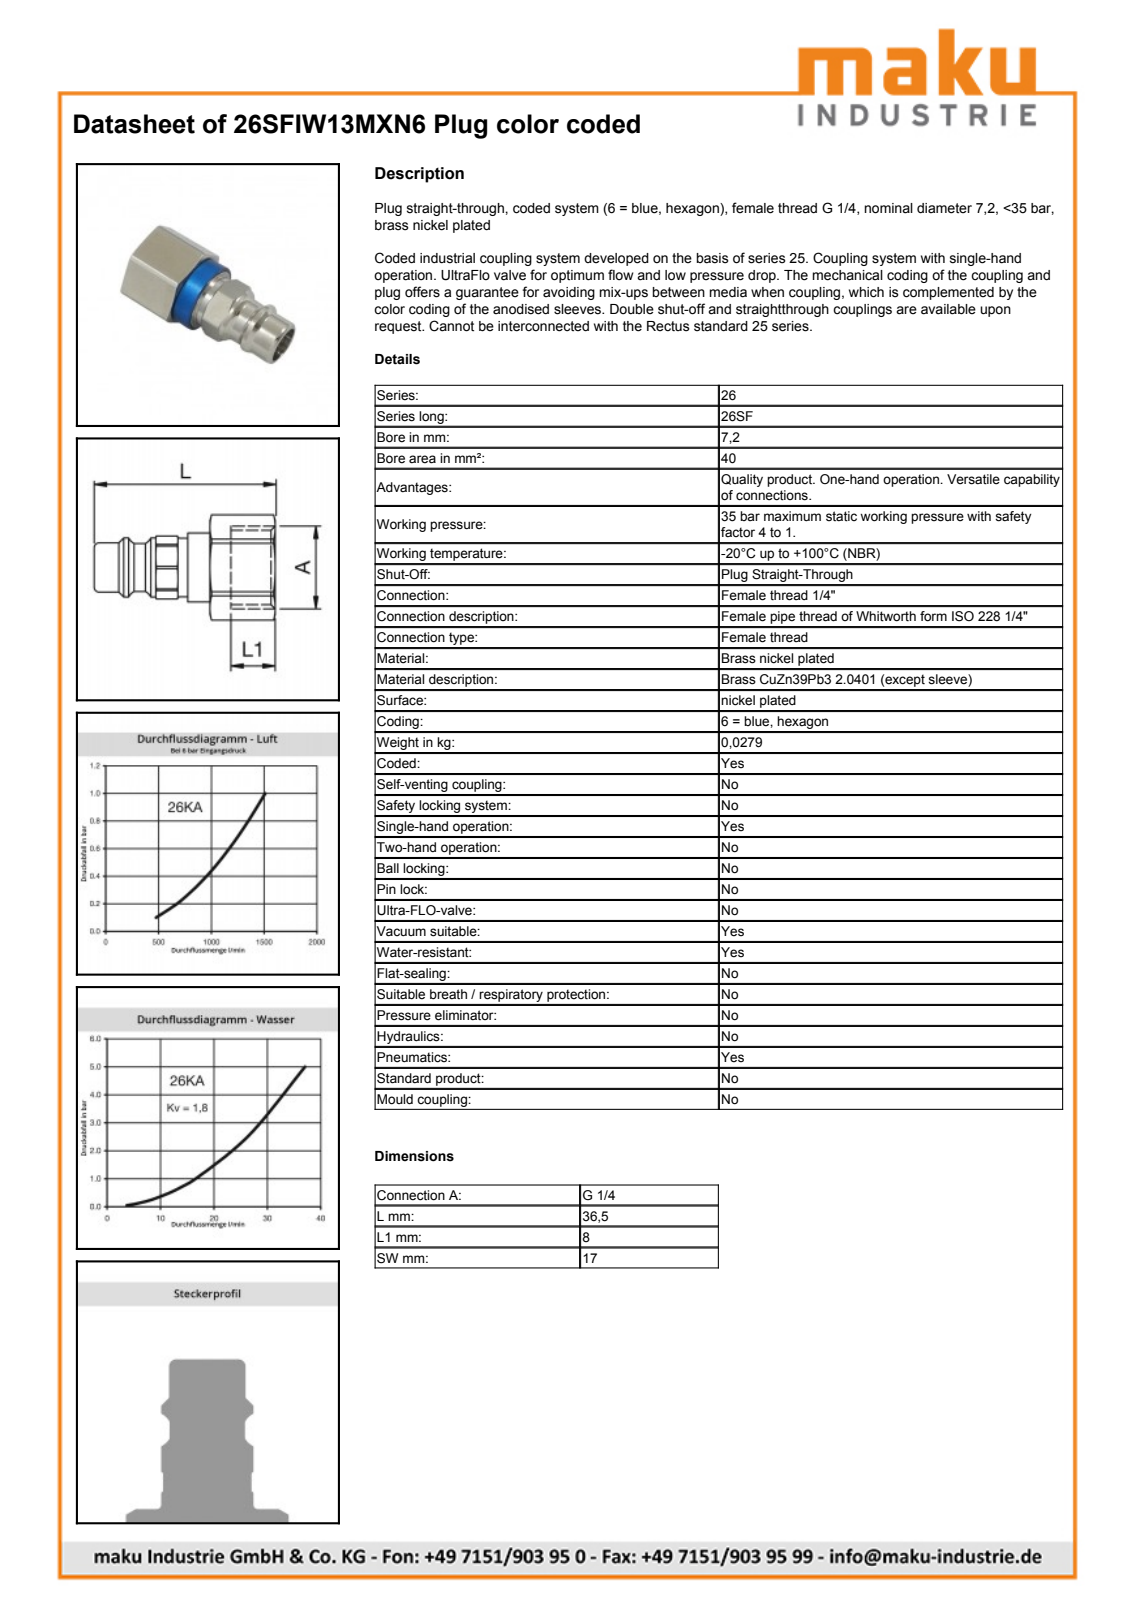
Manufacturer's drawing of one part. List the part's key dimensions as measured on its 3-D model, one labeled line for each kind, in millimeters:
Part name (STEP PRODUCT): D112680; D112677; D103012
STEP written by: Autodesk Inventor 2013 (AUTOMOTIVE_DESIGN)
Units: millimetres
Bodies: 2 solids, 75 faces (19 planar, 23 cylindrical, 33 other)
Overall size (bounding box): 36.5 × 19.15 × 17
Volume: 3 616 mm³ · Surface area: 3 477 mm²
Round holes (diameter × count): ⌀7.85 ×1, ⌀11.45 ×1, ⌀13.85 ×1, ⌀14.05 ×1
Round bosses / shafts (diameter × count): ⌀15.5 ×1, ⌀14 ×1, ⌀12 ×1, ⌀11.9 ×1, ⌀10 ×1, ⌀9.75 ×1
Partial cylindrical surfaces — rounded edges, fillets, slot ends (radius × count): R6.8 ×1, R9.57 ×1
Main face-to-face distances: 17, 2.5, 14.5, 12, 13, 4.5, 17.5, 7.5, 3, 10
